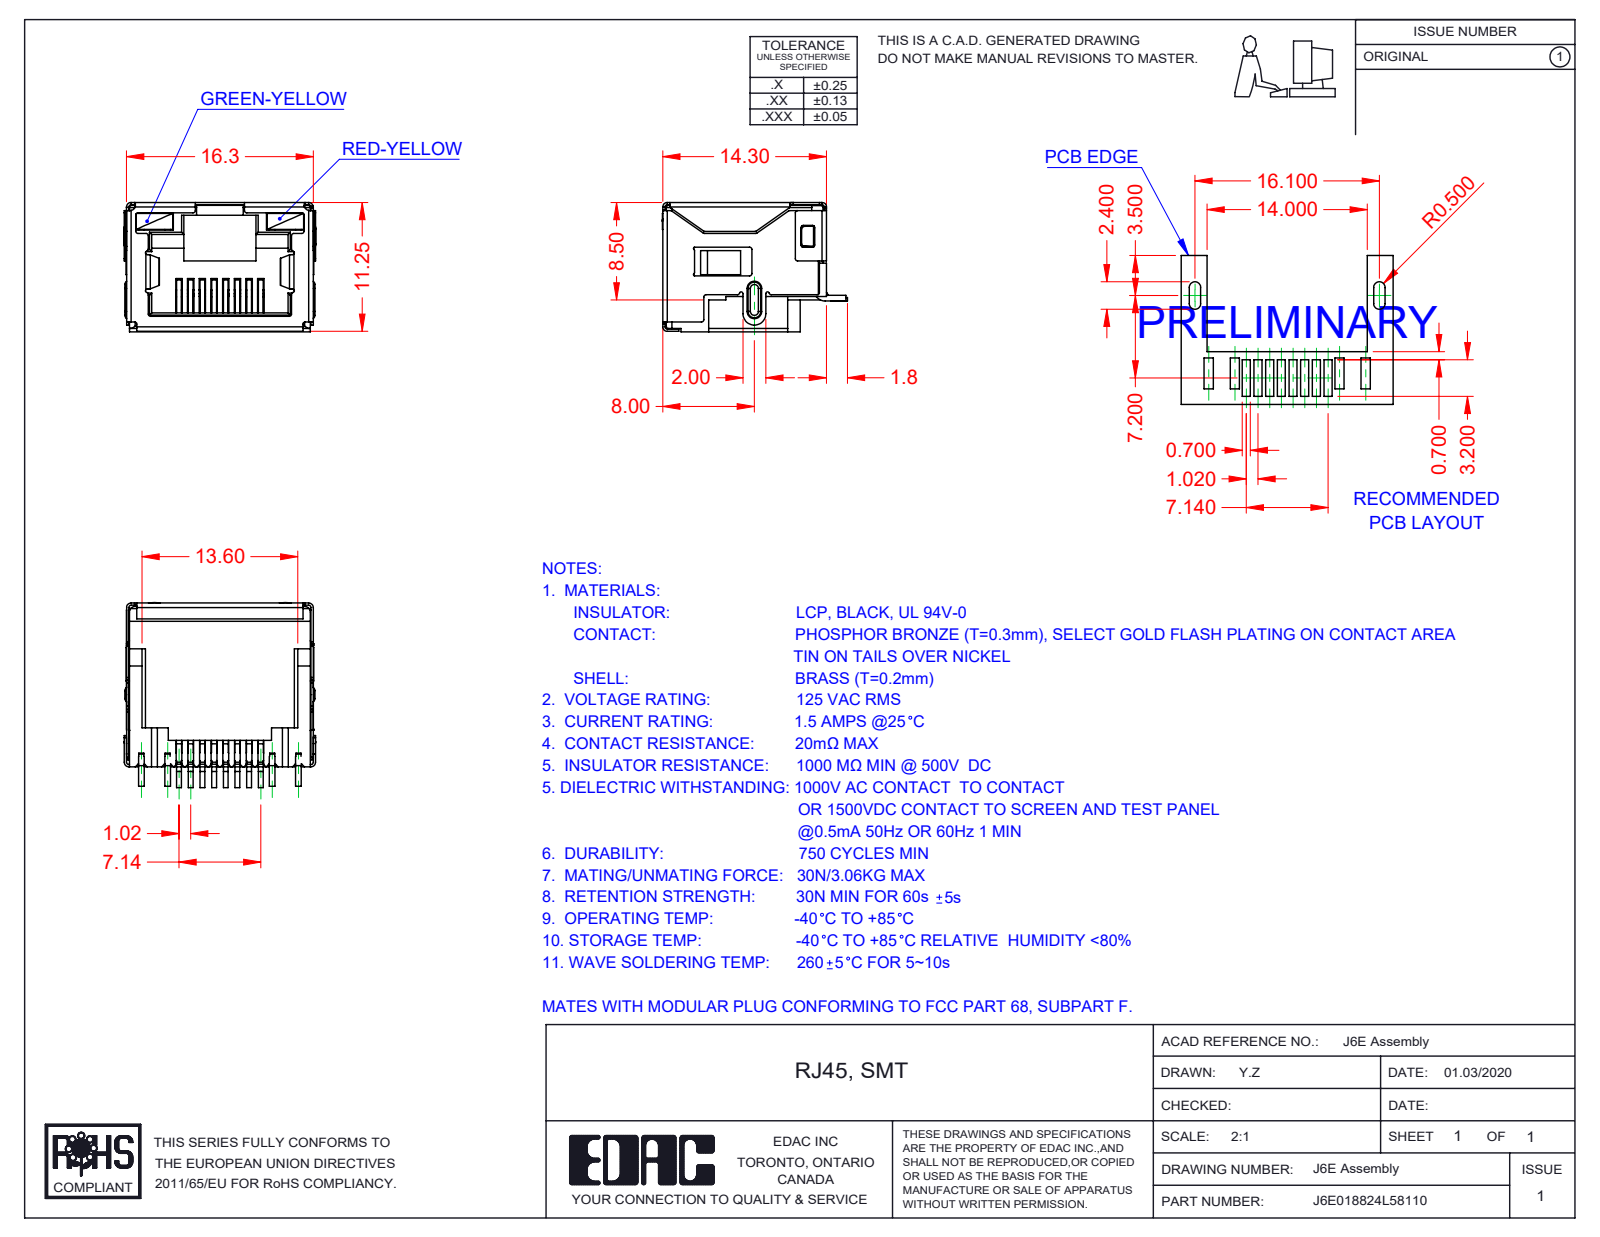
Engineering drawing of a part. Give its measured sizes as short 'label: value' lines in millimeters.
name: J6E018824L58110; 6E LED RH_8-Red-Yellow; 6E Contacts; 6E Shield_LED (+2 more)
written by: SolidWorks 2016 (CONFIG_CONTROL_DESIGN)
unit: mm
bodies: 12 solids, 1500 faces (1099 planar, 351 cylindrical, 50 other)
size: 16.75 × 16.15 × 11.3
volume: 1 109 mm³; area: 4 045 mm²
rounds: 82× R0.2, 17× R0.25, 13× R0.4, 13× R0.5, 10× R0.1, 7× R0.15, 4× R0.3, 3× R1
face distances: 11.05, 16.05, 16.1, 15.85, 11.1, 11.3, 2.4, 0.7, 9.85, 0.49
